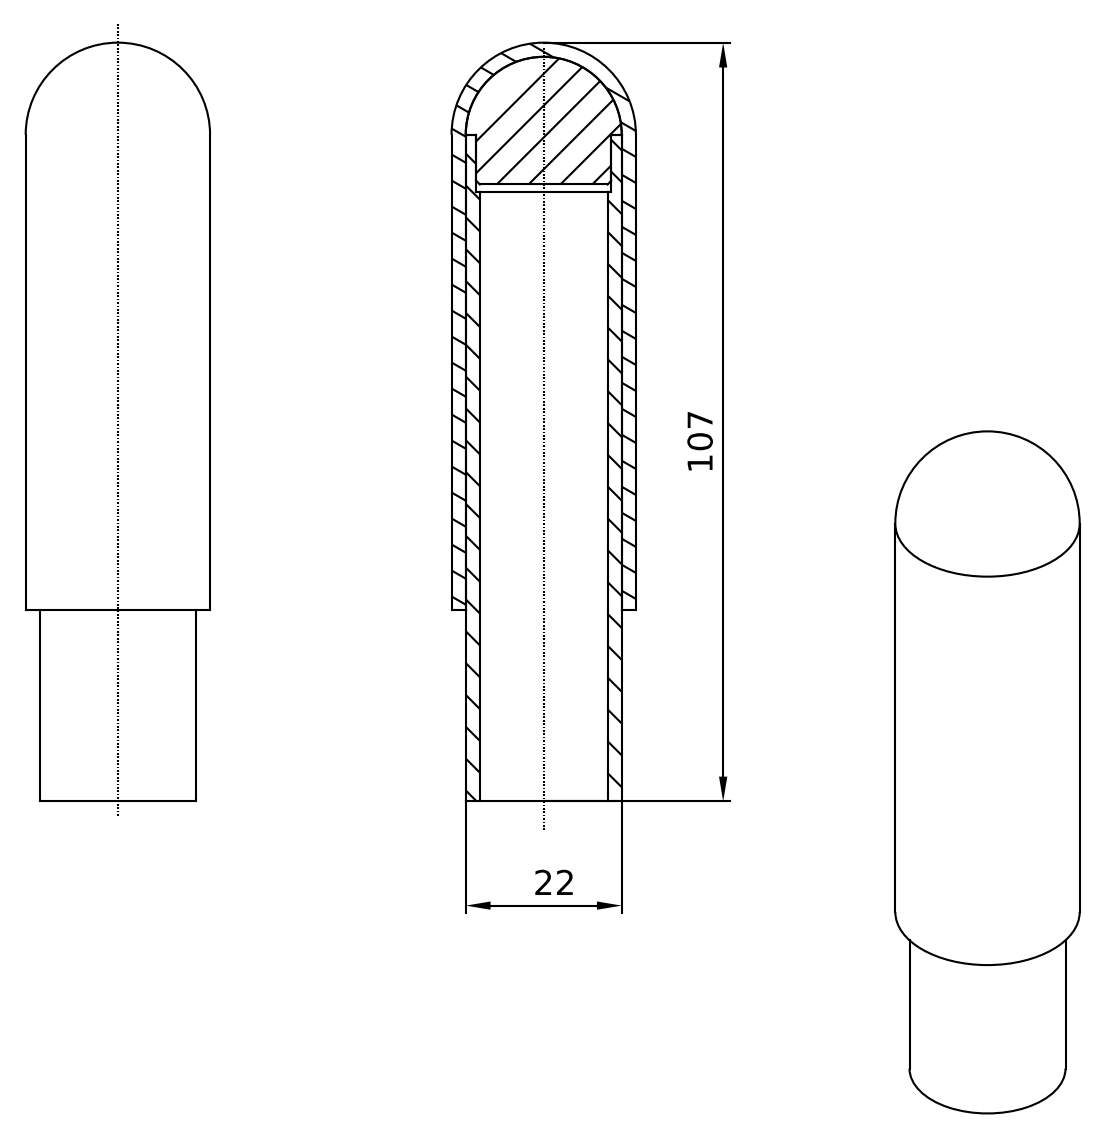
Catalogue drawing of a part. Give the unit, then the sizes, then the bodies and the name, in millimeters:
Units: millimetres
Overall size (bounding box): 107 × 26 × 26
Round holes (diameter × count): ⌀18 ×1, ⌀19 ×1
Round bosses / shafts (diameter × count): ⌀26 ×1, ⌀22 ×1
Main face-to-face distances: 60, 27, 87, 86, 59, 1
Volume: 28 262 mm³ · Surface area: 13 954 mm²
Bodies: 1 solid, 16 faces (4 planar, 8 cylindrical, 4 other)
STEP written by: Autodesk Inventor 8 (AUTOMOTIVE_DESIGN)
